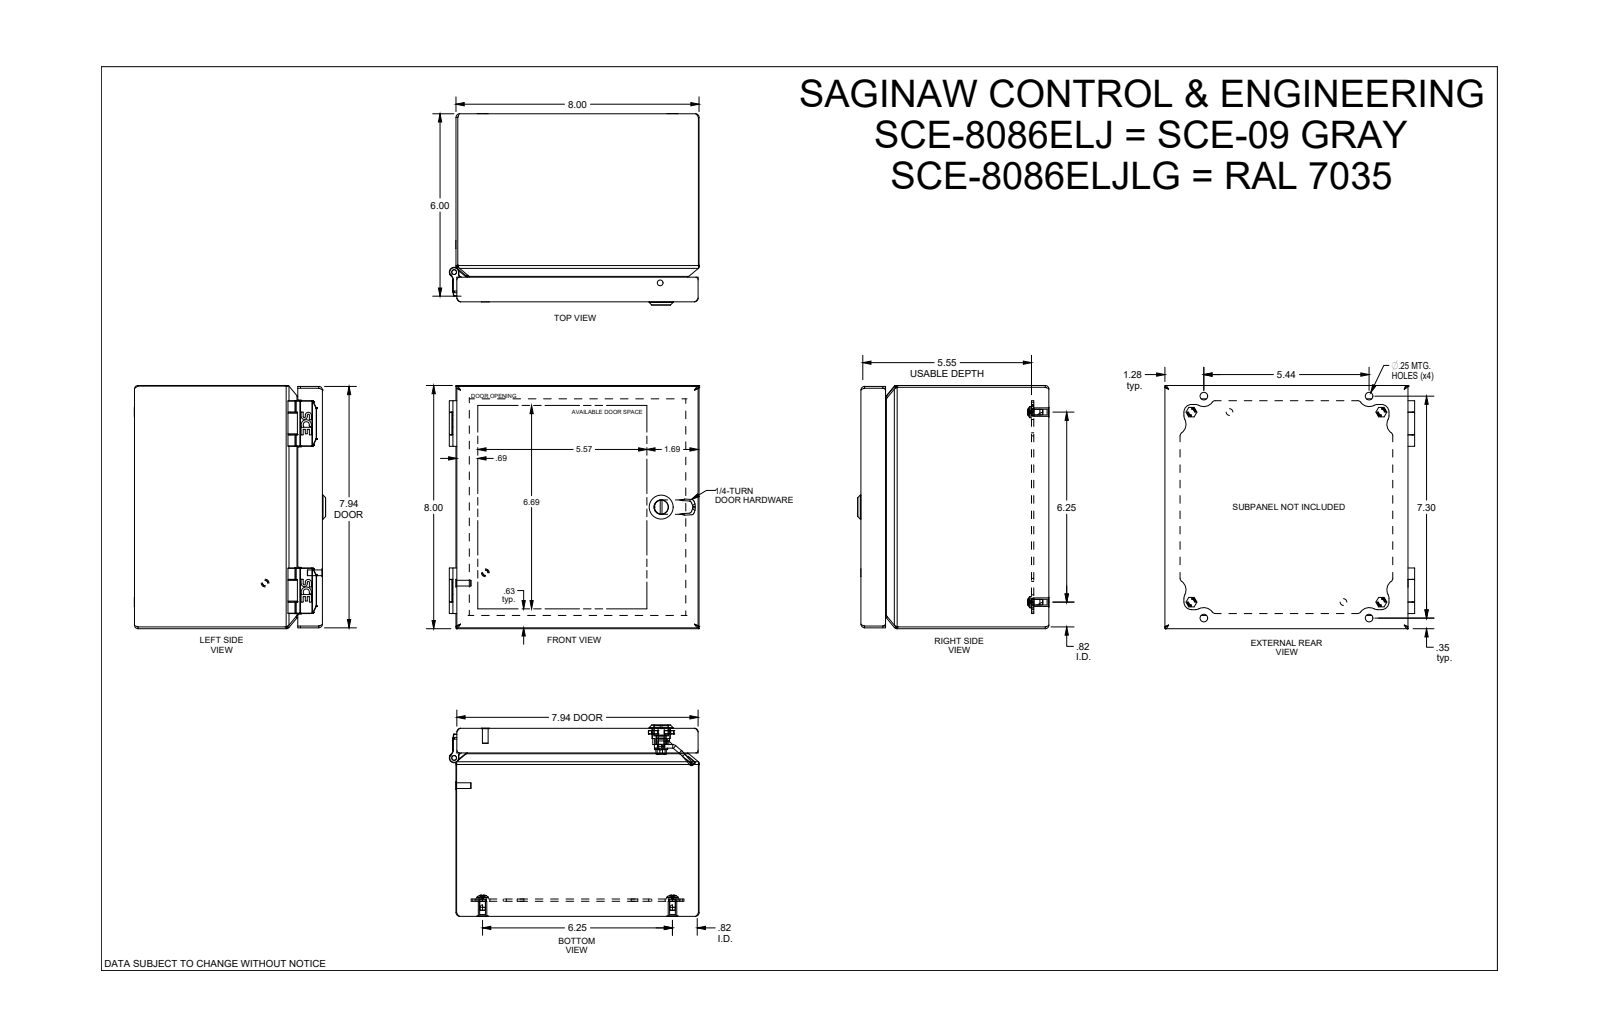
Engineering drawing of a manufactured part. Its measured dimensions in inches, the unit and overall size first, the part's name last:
Units: inches
Overall size (bounding box): 8.22 × 8 × 6.292
Round holes (diameter × count): ⌀0.25 ×4, ⌀0.284 ×4, ⌀0.17 ×2, ⌀0.218 ×2, ⌀0.158 ×1, ⌀0.2 ×1, ⌀0.239 ×1, ⌀0.254 ×1, ⌀0.269 ×1, ⌀0.282 ×1, ⌀0.326 ×1, ⌀0.475 ×1
Round bosses / shafts (diameter × count): ⌀0.188 ×5, ⌀0.373 ×4, ⌀0.284 ×4, ⌀0.479 ×2, ⌀0.26 ×2, ⌀0.1 ×2, ⌀0.02 ×2, ⌀0.788 ×1
Partial cylindrical surfaces — rounded edges, fillets, slot ends (radius × count): R0.106 ×66, R0.005 ×36, R0.008 ×32, R0.013 ×21, R0.05 ×16, R0.025 ×12, R0.25 ×12, R0.01 ×10
Main face-to-face distances: 0.059, 7.941, 0.062, 8, 7.882, 6.123, 6.185, 6.126, 6.064, 0.571
Hole centre spacings: 6.25, 1.25, 5, 3.148, 6.251, 6.374, 6.656, 8.004
Volume: 24.73 in³ · Surface area: 801.8 in²
Bodies: 22 solids, 1290 faces (401 planar, 386 cylindrical, 503 other)
Part name (STEP PRODUCT): SCE-8086ELJ
STEP written by: SolidWorks 2021 (AUTOMOTIVE_DESIGN)
